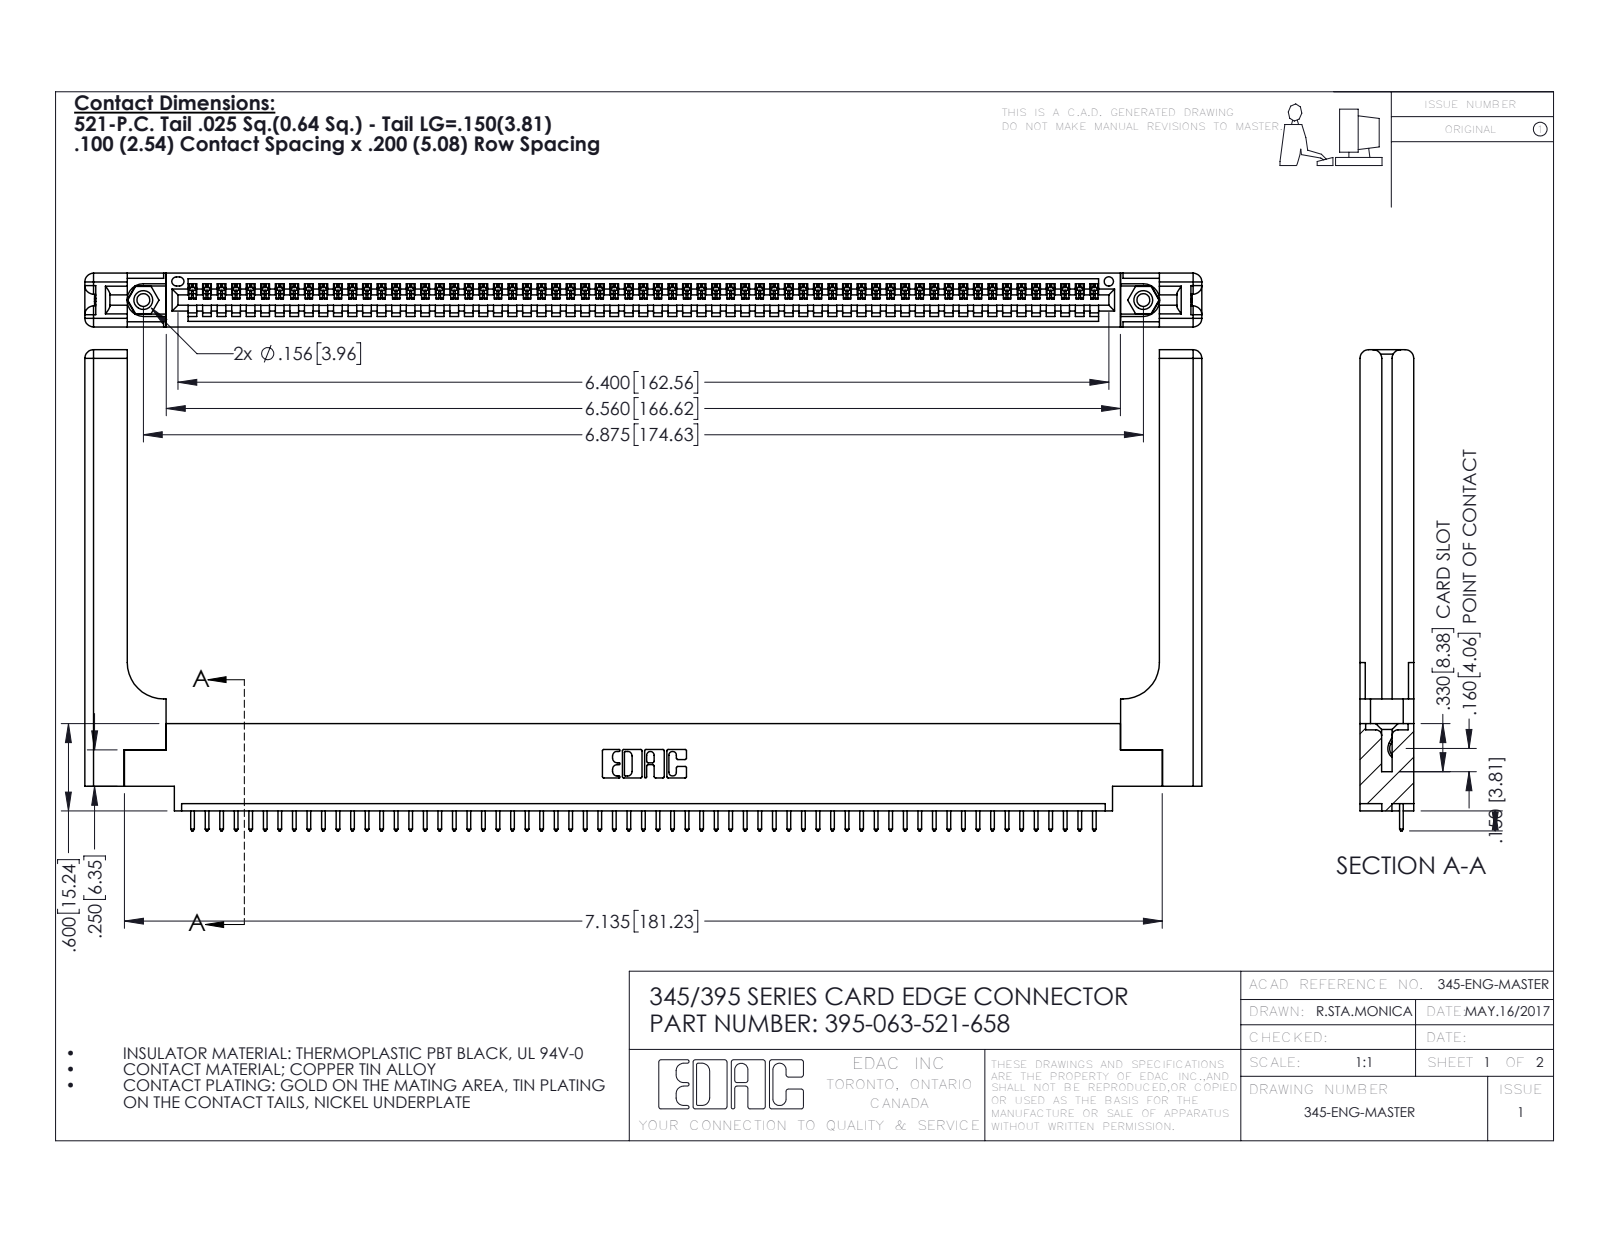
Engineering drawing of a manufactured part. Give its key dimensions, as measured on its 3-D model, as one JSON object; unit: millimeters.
{"part_name": "345 Part_0.170 Offset - 0.156 Dia-TH; 345-220-058_345-220-058; 395-063-521-658; 345-250-001_345-250-001-102 (+1 more)", "step_written_by": "SolidWorks 2016 (CONFIG_CONTROL_DESIGN)", "units": "millimeters", "bodies": {"solids": 68, "faces": 4040, "planar": 2752, "cylindrical": 1228, "other": 60}, "overall_size": [195, 84, 9.4], "volume_mm3": 26910, "surface_area_mm2": 29480, "round_holes": [[2.3, 2], [3.2, 2], [4, 2], [1.6, 1]], "round_bosses_or_shafts": [[3.9, 2]], "partial_cylinders_radius": [[0.2, 126], [0.3, 126], [0.3, 22], [1.5, 16], [0.2, 6], [0.8, 6], [0.7, 3], [0.8, 2]], "face_to_face_distances": [1.8, 9.4, 7.6, 2.5, 6.9, 0.6, 5.1, 5.7, 3.8, 3.8], "hole_center_spacings": [6.9, 168.6, 174.6]}
